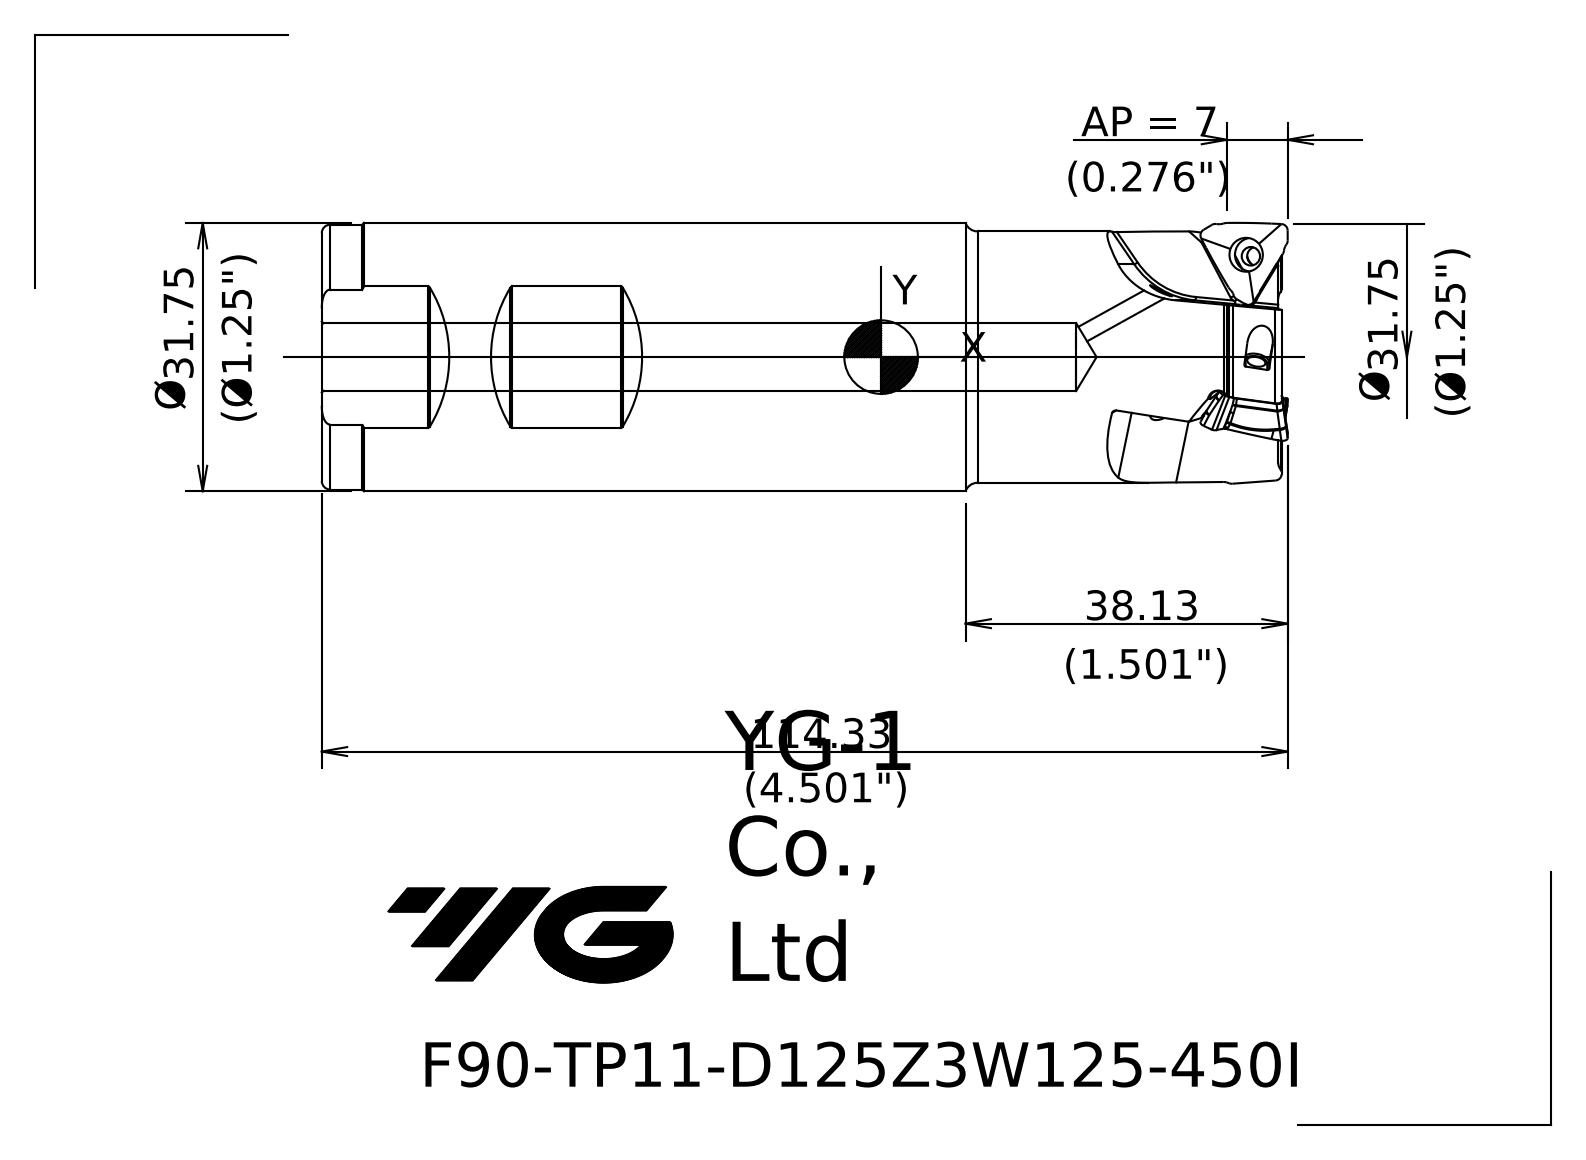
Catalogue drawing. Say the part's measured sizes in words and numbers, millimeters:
The part is named "1022494C9345nm7u". Its 3-D file was written by "SIEMENS PLM Software NX 10.0 (AP203_CONFIGURATION_CONTROLLED_3D_DESIGN_OF_MECHANICAL_PARTS_AND_ASSEMBLIES_MIM_LF)". It is 1 solid with 54 faces: 8 planar, 8 cylindrical and 38 other. Overall it measures 116.95 by 31.93 by 31.93 millimeters. Its volume is 80 760 cubic millimeters and its surface area 17 232 square millimeters. Round holes: 1 of diameter 1.5, 1 of diameter 8. Round bosses or shafts: 1 of diameter 31.75, 1 of diameter 31.35, 1 of diameter 29.75. Partial cylindrical surfaces (rounded edges, fillets, slot ends): 3 of radius 0.3. The main face-to-face distances are 113.2, 16.14, 0.4, 113.6.
